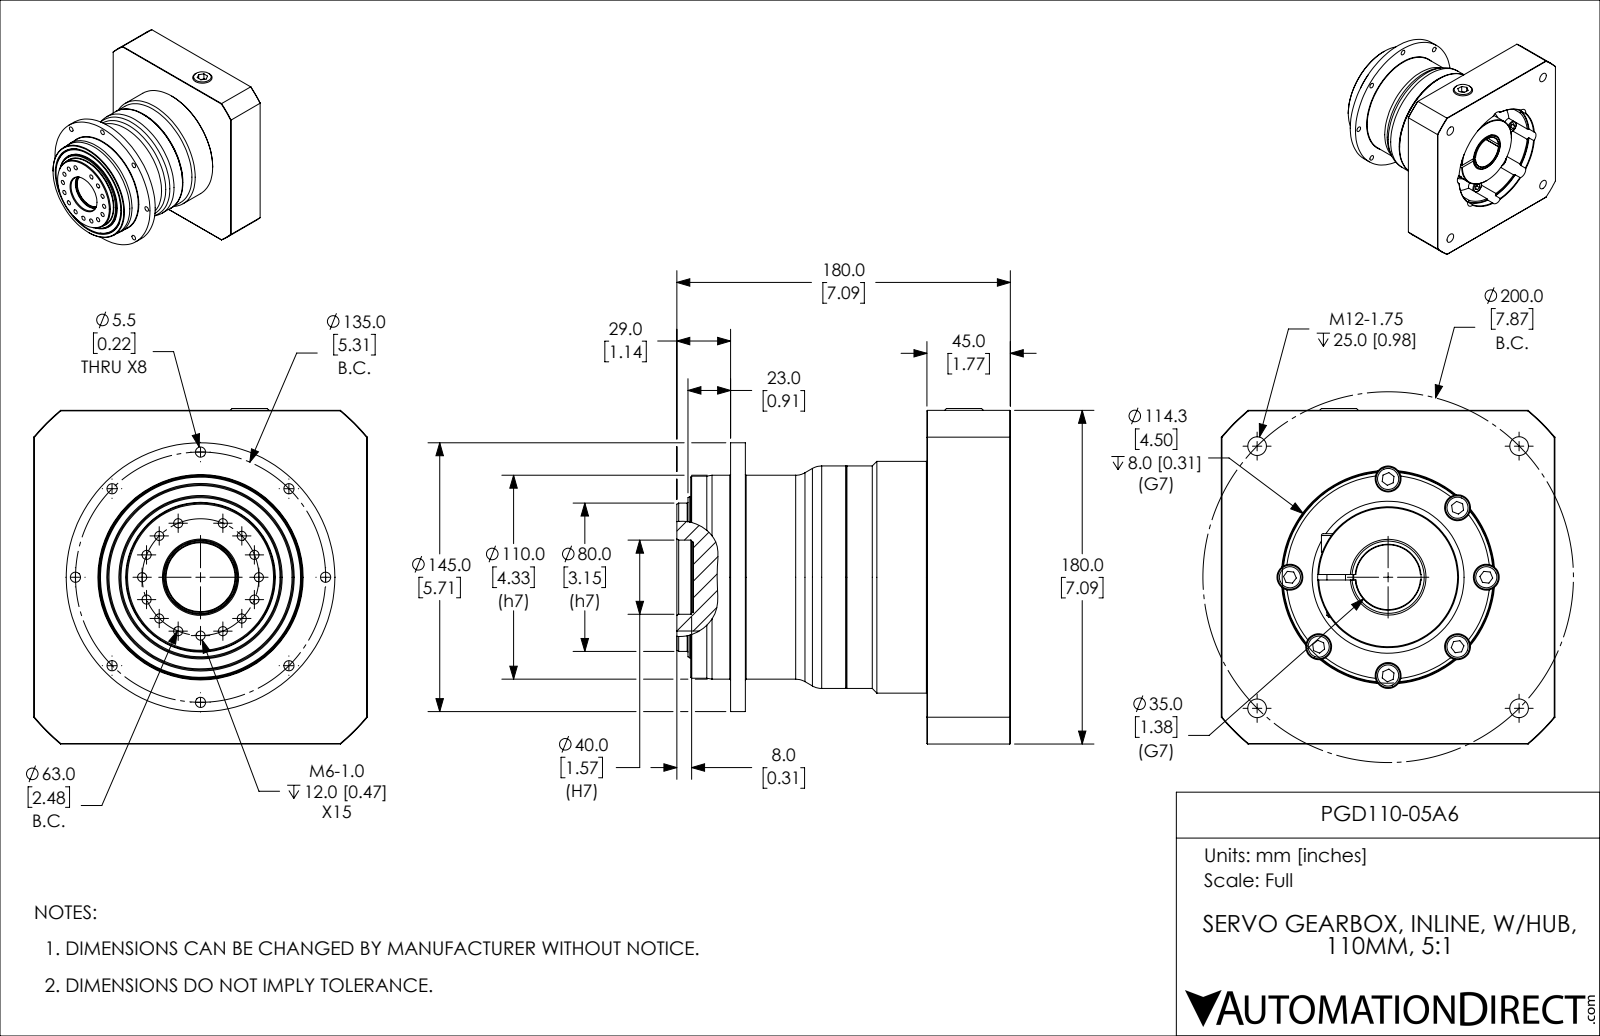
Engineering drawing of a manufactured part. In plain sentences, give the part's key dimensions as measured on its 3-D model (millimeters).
The part is named "PGD110-05A6". Its 3-D file was written by "SolidWorks 2015 (AUTOMOTIVE_DESIGN)". It is 6 solids with 410 faces: 150 planar, 180 cylindrical and 80 other. Overall it measures 180.4 by 180 by 179.4 millimeters. Its volume is 2 496 000 cubic millimeters and its surface area 235 890 square millimeters. Round holes: 11 of diameter 4.92, 8 of diameter 5.5, 4 of diameter 4.92, 4 of diameter 10.11, 2 of diameter 11, 1 of diameter 10, 1 of diameter 16, 1 of diameter 17.5, 1 of diameter 35, 1 of diameter 37.2, 1 of diameter 39.2, 1 of diameter 110. Round bosses or shafts: 7 of diameter 13, 1 of diameter 145, 1 of diameter 125, 1 of diameter 120, 1 of diameter 109, 1 of diameter 80, 1 of diameter 72, 1 of diameter 42. Partial cylindrical surfaces (rounded edges, fillets, slot ends): 7 of radius 7, 1 of radius 8.75, 1 of radius 57.65, 1 of radius 117.2. The main face-to-face distances are 104.2, 45, 59.2, 179.4, 173, 128, 68.8, 4, 22, 26. The hole center spacings are 40.25, 62.62, 84.71, 97.35, 12.29, 52.38, 74.49, 44.54.
